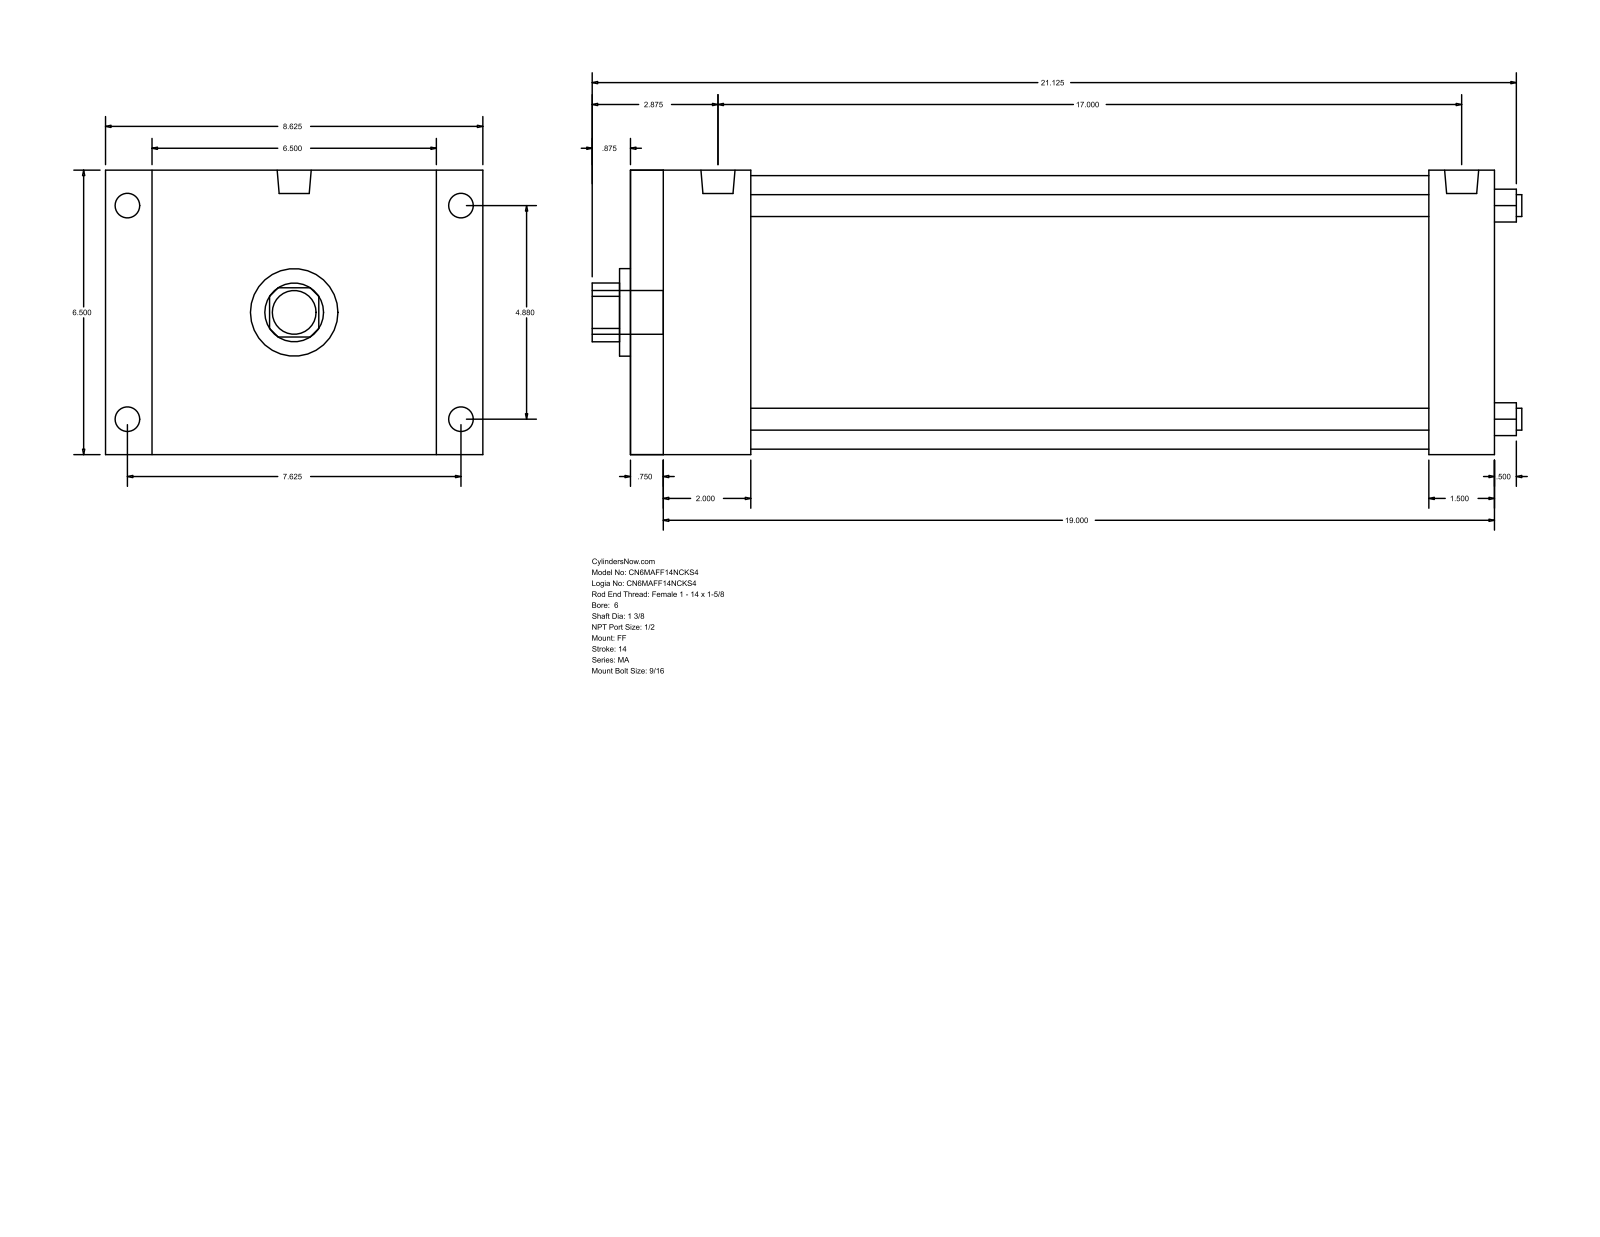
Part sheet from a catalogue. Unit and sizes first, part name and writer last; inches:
Units: inches
Overall size (bounding box): 21.25 × 8.625 × 6.5
Round holes (diameter × count): ⌀0.5 ×4, ⌀1.375 ×1, ⌀2 ×1, ⌀6.25 ×1
Round bosses / shafts (diameter × count): ⌀0.687 ×4, ⌀0.563 ×4, ⌀0.778 ×2, ⌀1 ×1
Partial cylindrical surfaces — rounded edges, fillets, slot ends (radius × count): R0.672 ×1
Main face-to-face distances: 6.5, 19.75, 0.625, 19.125, 2.625, 2, 17.125, 18.25, 17.625, 15.625
Hole centre spacings: 3.451, 4.88, 6.902
Bodies: 0 solids, 92 faces (64 planar, 28 cylindrical, 0 other)
Part name (STEP PRODUCT): MA_FF__0600_1.375
STEP written by: GSSL Pune (CONFIG_CONTROL_DESIGN)
